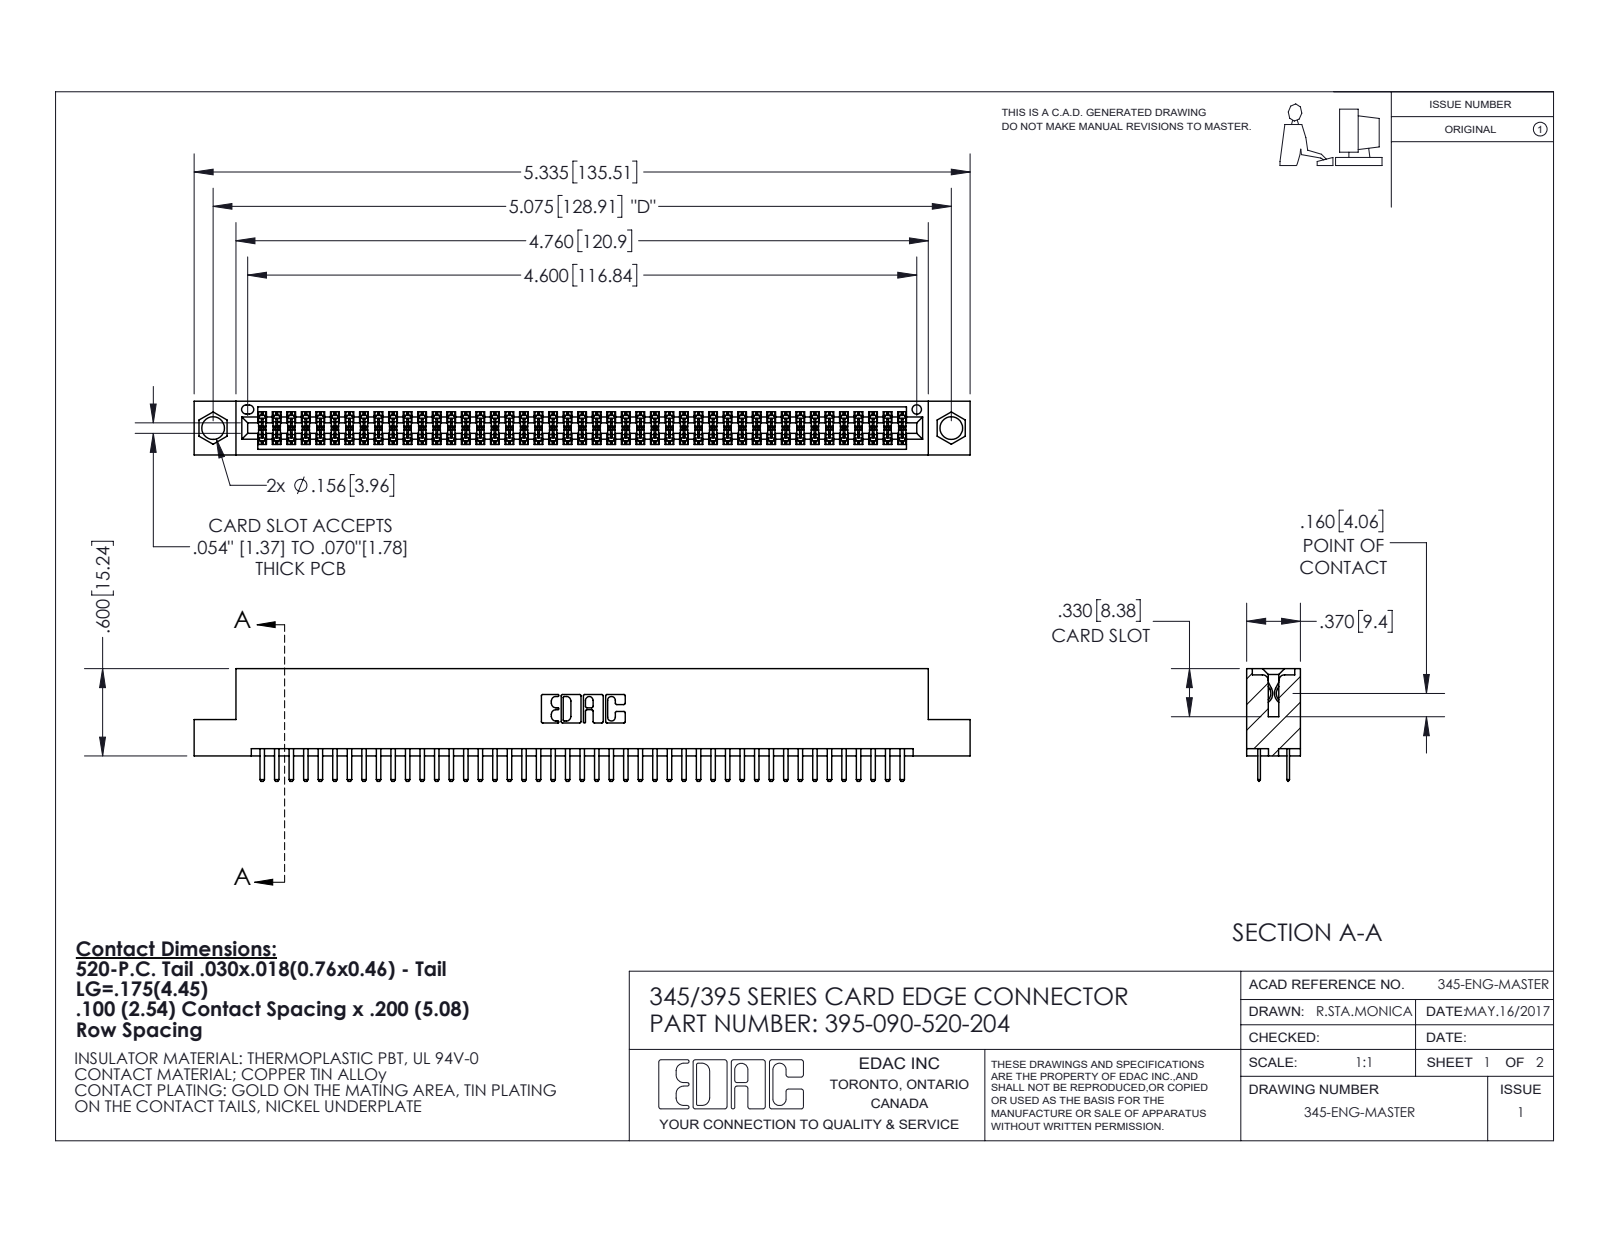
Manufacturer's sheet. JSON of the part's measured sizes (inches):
{"part_name": "395-090-520-204; 345-292-001_345-293-120; 345 Part_Flush Mounting Lugs - 0.156 Dia-TI", "step_written_by": "SolidWorks 2020 (CONFIG_CONTROL_DESIGN)", "units": "inches", "bodies": {"solids": 91, "faces": 5000, "planar": 3244, "cylindrical": 1756, "other": 0}, "overall_size": [5.335, 0.775, 0.37], "volume_in3": 0.796, "surface_area_in2": 29.62, "round_holes": [[0.156, 2], [0.064, 1]], "partial_cylinders_radius": [[0.006, 180], [0.01, 94], [0.01, 22], [0.007, 6], [0.031, 6], [0.026, 3], [0.014, 2], [0.019, 2]], "face_to_face_distances": [0.072, 0.298, 0.2, 0.37, 0.098, 0.272, 0.025, 0.225, 0.022, 0.072], "hole_center_spacings": [0.27, 4.839, 5.075]}
